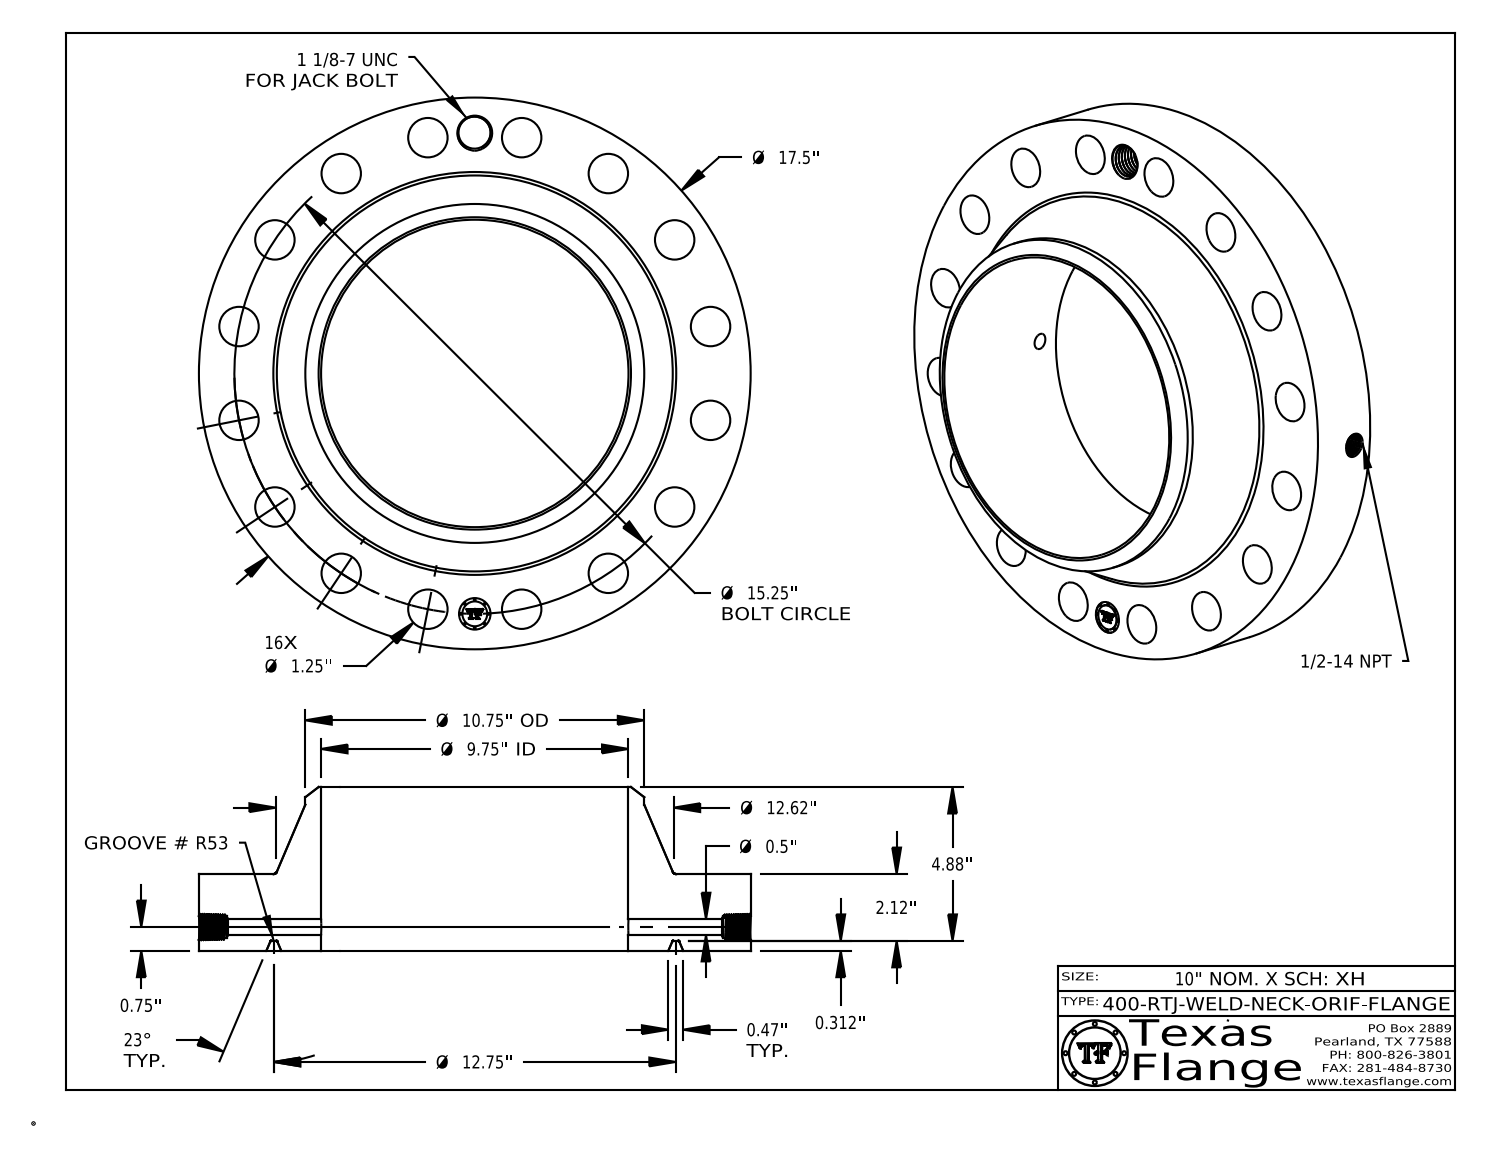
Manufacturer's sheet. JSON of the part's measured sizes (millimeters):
{"part_name": "400-RTJ-WELD-NECK", "step_written_by": "CATIA V5 STEP AP214 (AUTOMOTIVE_DESIGN)", "units": "millimeters", "bodies": {"solids": 1, "faces": 806, "planar": 370, "cylindrical": 112, "other": 324}, "overall_size": [444.5, 444.5, 131.9], "volume_mm3": 6987000, "surface_area_mm2": 544300, "round_holes": [[31.8, 16], [12.7, 1], [17.1, 1], [25, 1], [25.4, 1], [247.7, 1]], "round_bosses_or_shafts": [[1.5, 8], [444.5, 1], [273.1, 1], [20, 1]], "face_to_face_distances": [61.8, 7.9, 53.8, 131.9, 124, 70.1, 0.4, 61.4, 53.5, 70.5], "hole_center_spacings": [148.2, 193.7, 273.9, 357.9, 379.9, 75.6, 75.6, 215.2]}
